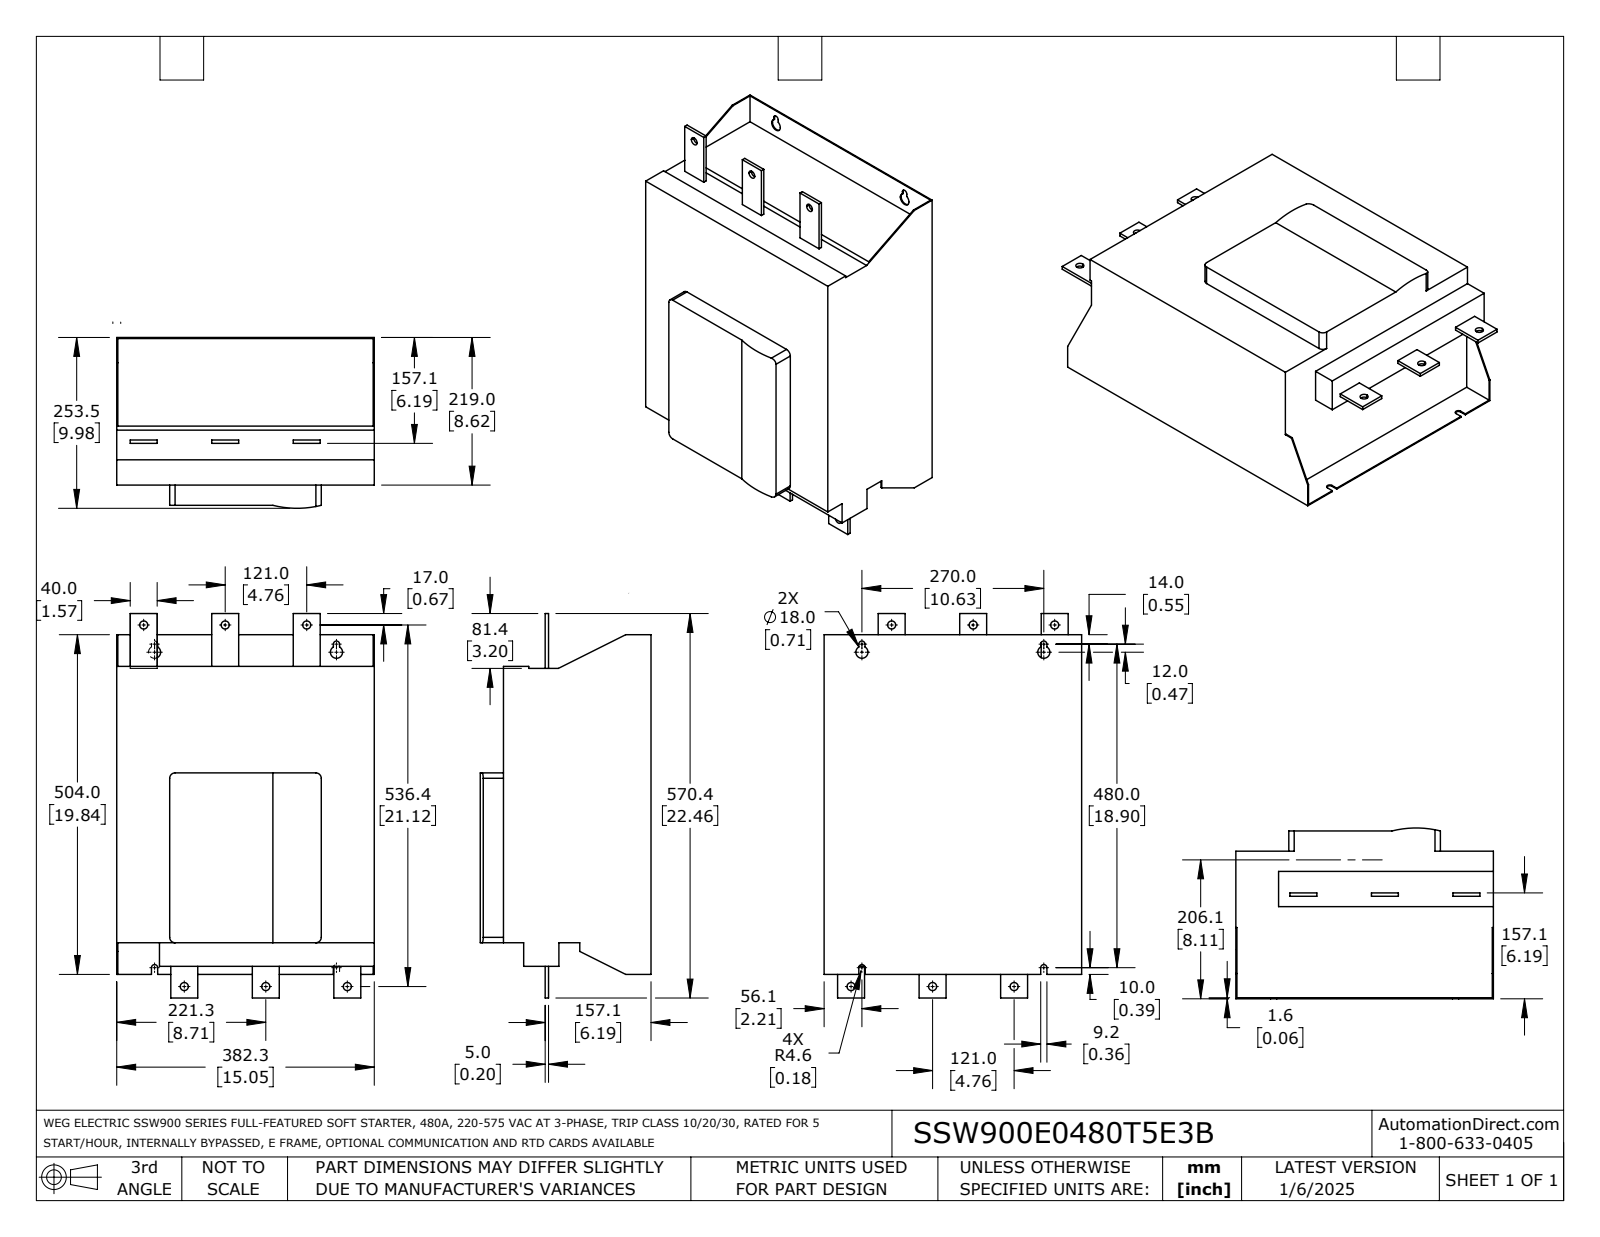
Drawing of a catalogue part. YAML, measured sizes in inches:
part_name: "SSW900E0480T5E3B"
step_written_by: "SolidWorks 2021 (AUTOMOTIVE_DESIGN)"
units: inches
bodies: {solids: 1, faces: 97, planar: 70, cylindrical: 27, other: 0}
overall_size: [22.457, 15.049, 9.979]
volume: 2243
surface_area: 1320
round_holes:
  - {diameter: 0.472, count: 6}
  - {diameter: 0.709, count: 2}
partial_cylinders:
  - {radius: 0.181, count: 4}
  - {radius: 0.315, count: 4}
  - {radius: 5.788, count: 1}
face_to_face_distances: [8.622, 15.049, 16.142, 0.063, 1.181, 9.803, 8.559, 9.74, 1.378, 16.024]
hole_center_spacings: [4.764, 21.251, 9.528, 21.253, 22.291, 1.713, 2.356, 4.424]
